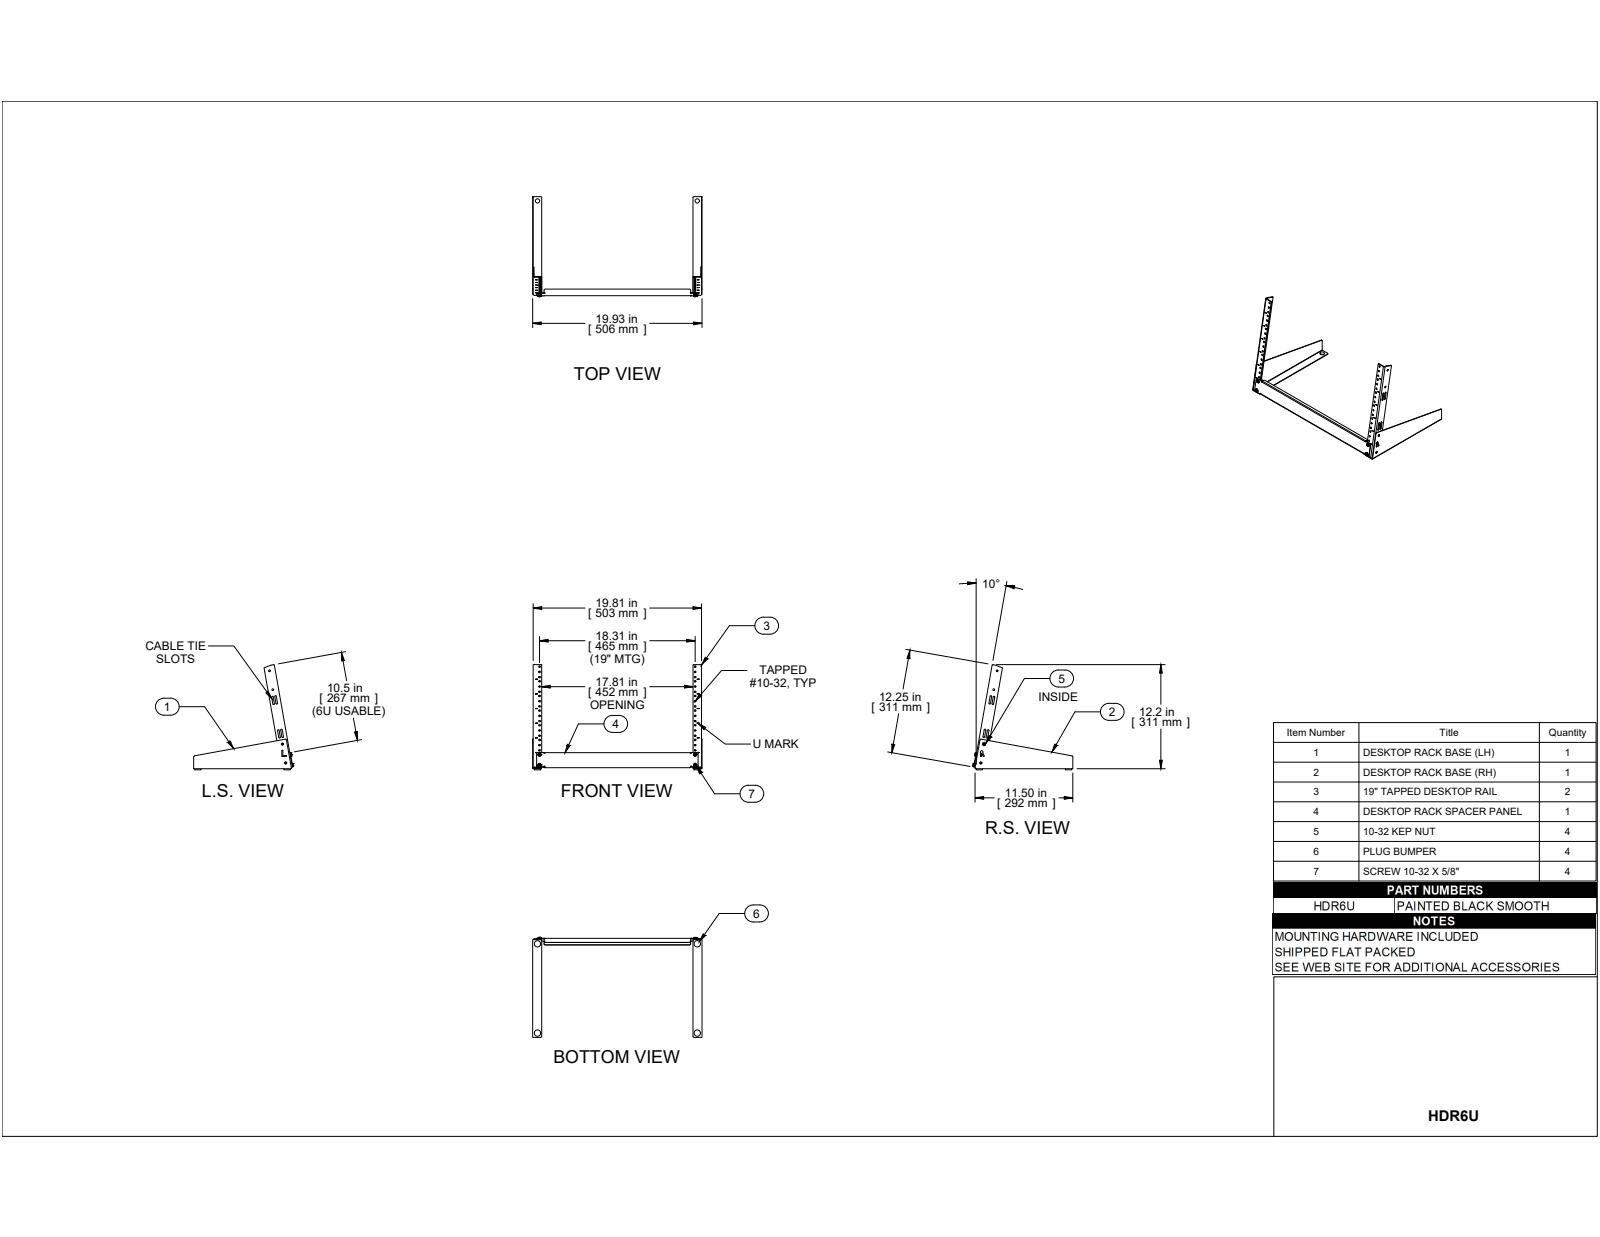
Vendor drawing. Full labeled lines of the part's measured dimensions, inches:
Part name (STEP PRODUCT): HDR6UBK
STEP written by: SolidWorks 2019 (CONFIG_CONTROL_DESIGN)
Units: inches
Bodies: 21 solids, 432 faces (276 planar, 148 cylindrical, 8 other)
Overall size (bounding box): 19.926 × 12.374 × 11.773
Volume: 12.29 in³ · Surface area: 376.1 in²
Round holes (diameter × count): ⌀0.177 ×42, ⌀0.198 ×4, ⌀0.206 ×4, ⌀0.5 ×4, ⌀0.156 ×2, ⌀0.189 ×2
Round bosses / shafts (diameter × count): ⌀0.368 ×8, ⌀0.75 ×4, ⌀0.189 ×4, ⌀0.256 ×2, ⌀0.19 ×2
Partial cylindrical surfaces — rounded edges, fillets, slot ends (radius × count): R0.125 ×15, R0.094 ×8, R0.062 ×5, R0.029 ×4, R0.086 ×4, R0.048 ×2, R0.063 ×2, R0.143 ×2
Main face-to-face distances: 0.057, 19.87, 19.813, 0.095, 19.927, 0.152, 1.661, 0.152, 19.718, 19.775
Hole centre spacings: 1.125, 3.5, 18.396, 1.75, 18.644, 18.323, 7, 18.347
